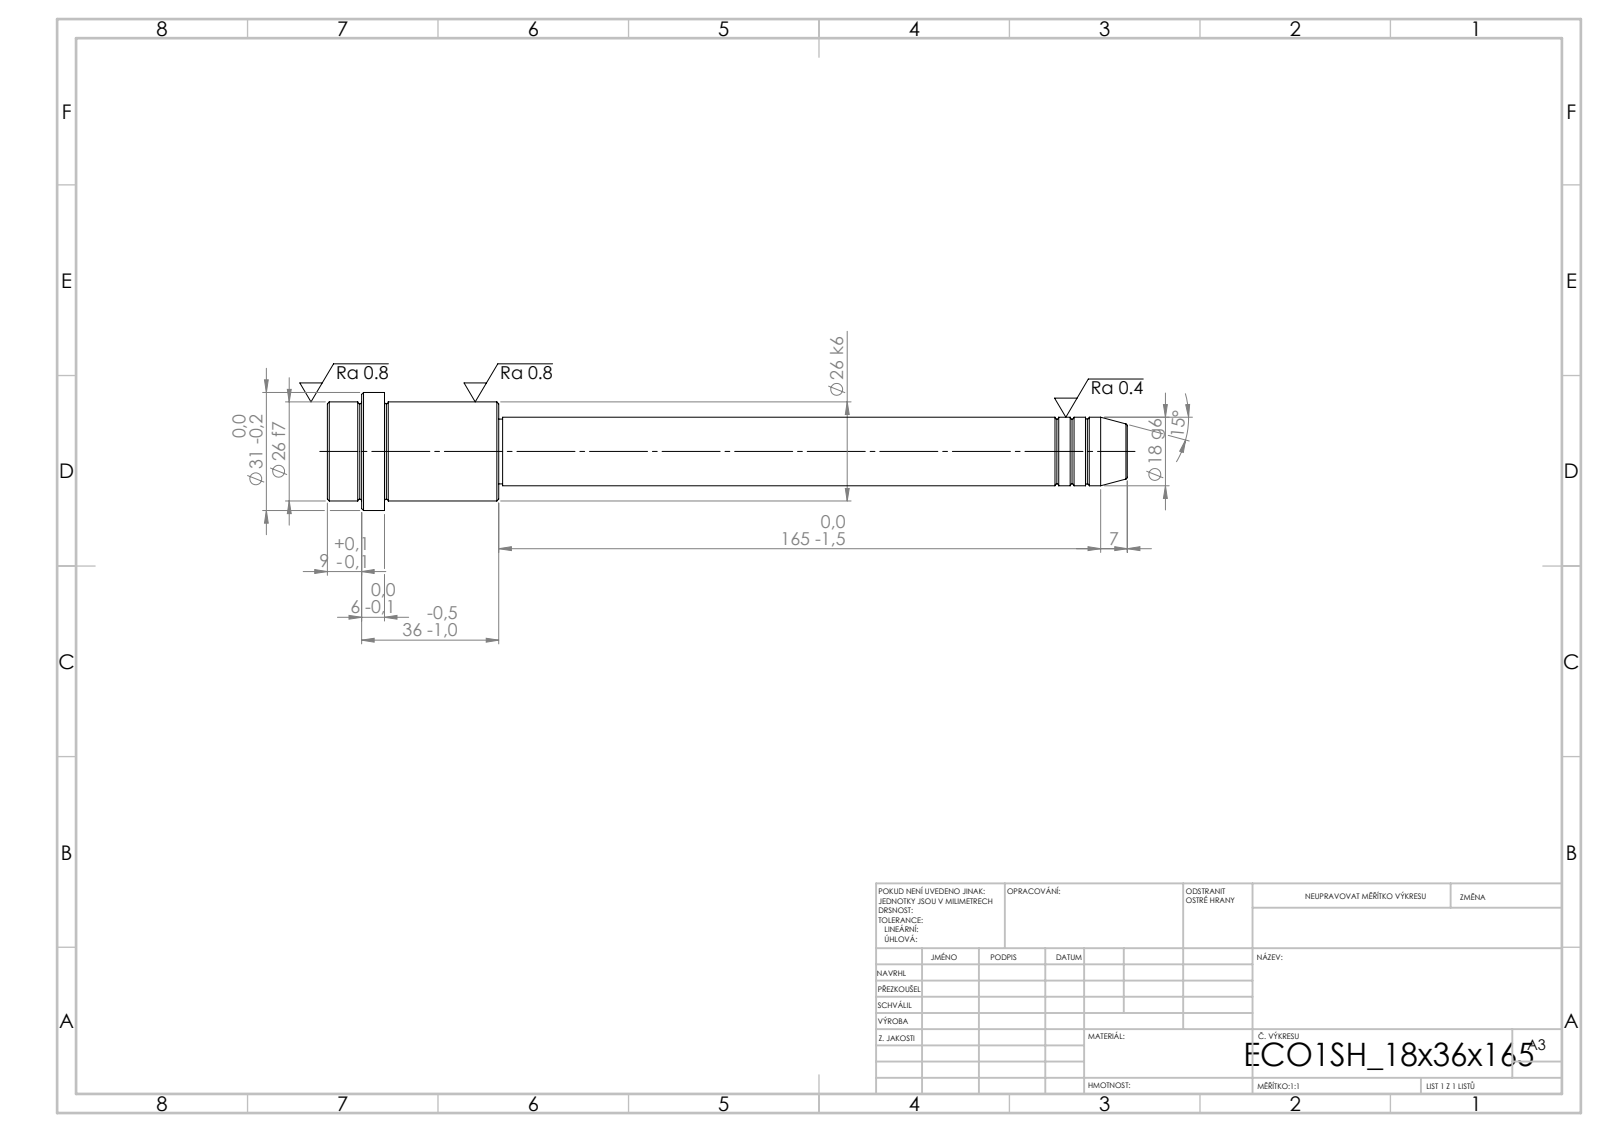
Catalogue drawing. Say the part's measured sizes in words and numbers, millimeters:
Its 3-D file was written by "SolidWorks 2019 (CONFIG_CONTROL_DESIGN)". It is 1 solid with 52 faces: 6 planar, 16 cylindrical and 30 other. Overall it measures 210 by 31 by 31 millimeters. Its volume is 66 688 cubic millimeters and its surface area 14 630 square millimeters. Round bosses or shafts: 1 of diameter 31, 1 of diameter 26, 1 of diameter 18, 1 of diameter 17. The main face-to-face distances are 45, 30, 15, 36, 6, 9, 165, 195, 201, 210.
